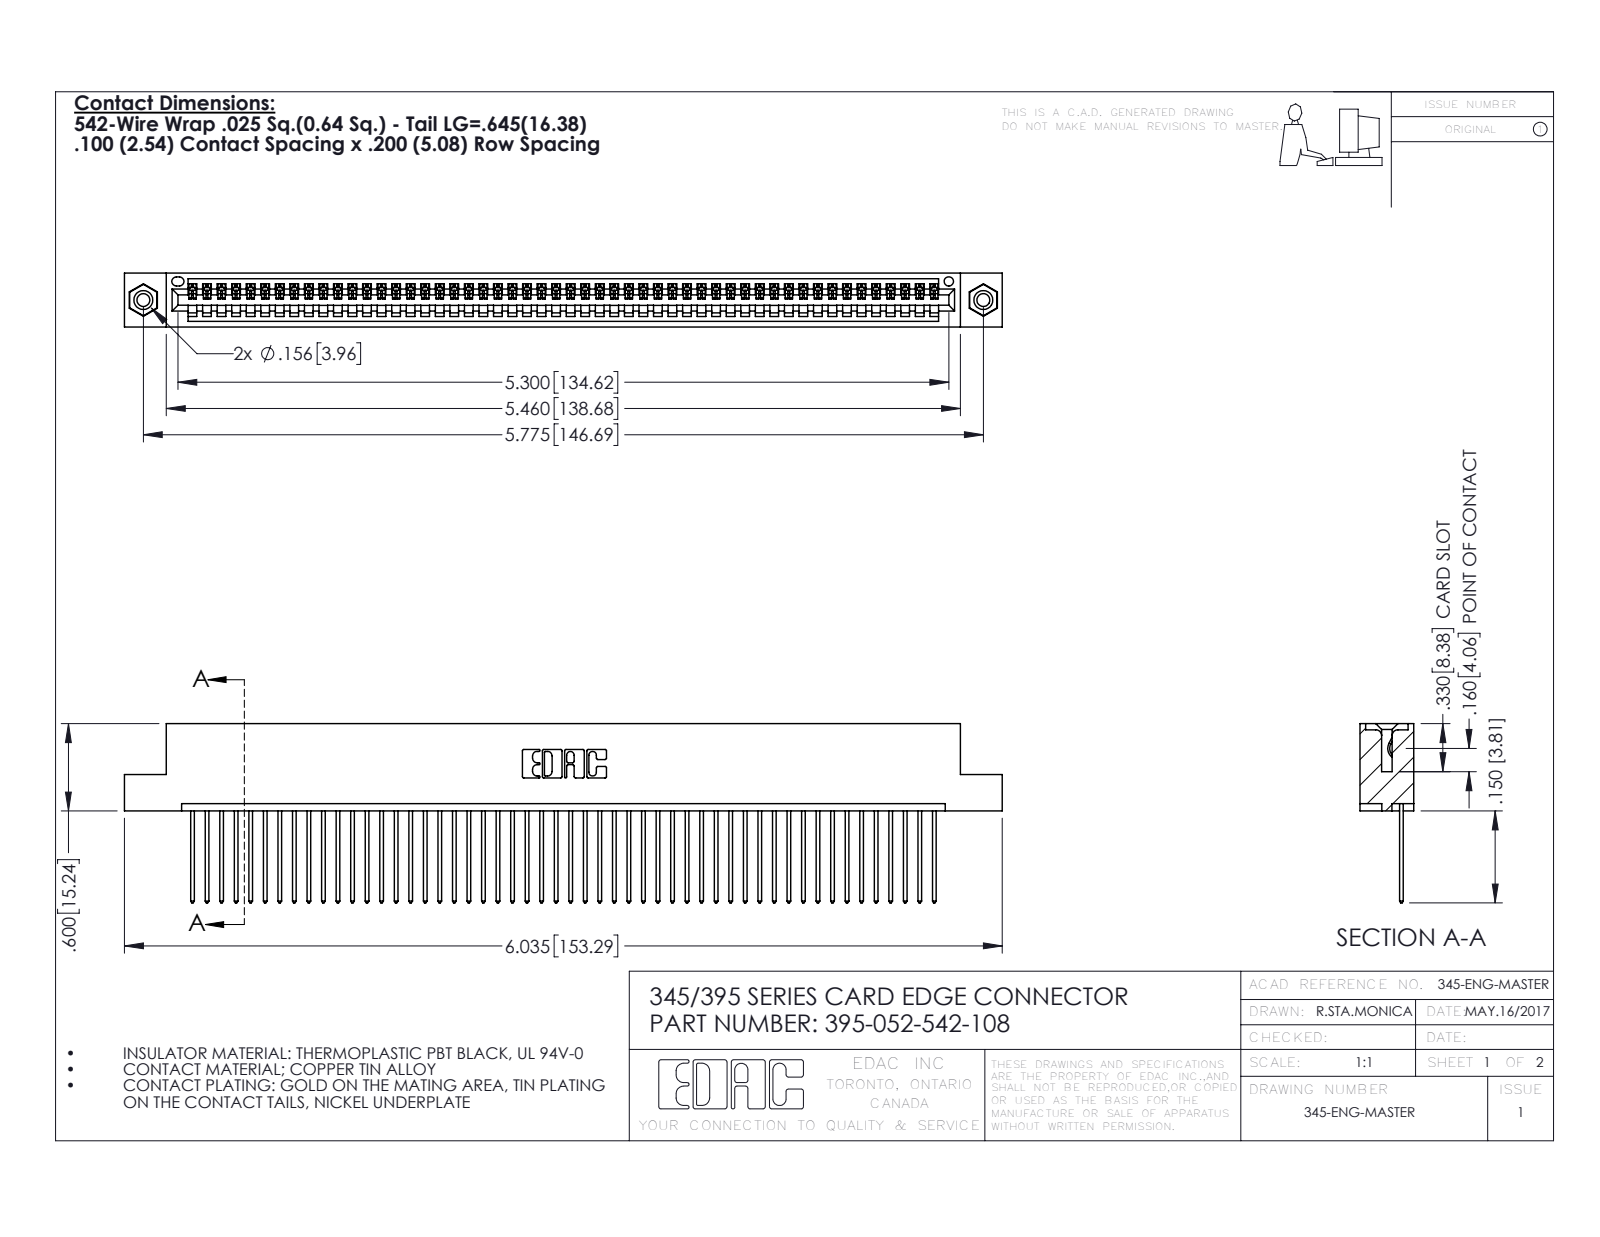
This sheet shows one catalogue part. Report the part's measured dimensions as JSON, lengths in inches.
{"part_name": "345 Part_Flush Mounting Lugs - 0.156 Dia-TI; 345-292-001_345-293-142; 395-052-542-108; 345-250-001_345-250-003-102", "step_written_by": "SolidWorks 2016 (CONFIG_CONTROL_DESIGN)", "units": "inches", "bodies": {"solids": 55, "faces": 3202, "planar": 2192, "cylindrical": 994, "other": 16}, "overall_size": [6.035, 1.232, 0.37], "volume_in3": 0.9, "surface_area_in2": 31.76, "round_holes": [[0.089, 2], [0.125, 2], [0.156, 2], [0.064, 1]], "round_bosses_or_shafts": [[0.155, 2]], "partial_cylinders_radius": [[0.006, 104], [0.01, 104], [0.01, 22], [0.007, 6], [0.031, 6], [0.026, 3], [0.031, 2], [0.04, 2]], "face_to_face_distances": [0.072, 0.298, 0.098, 0.272, 0.025, 0.37, 0.2, 0.225, 0.149, 0.072], "hole_center_spacings": [0.27, 5.539, 5.775]}
